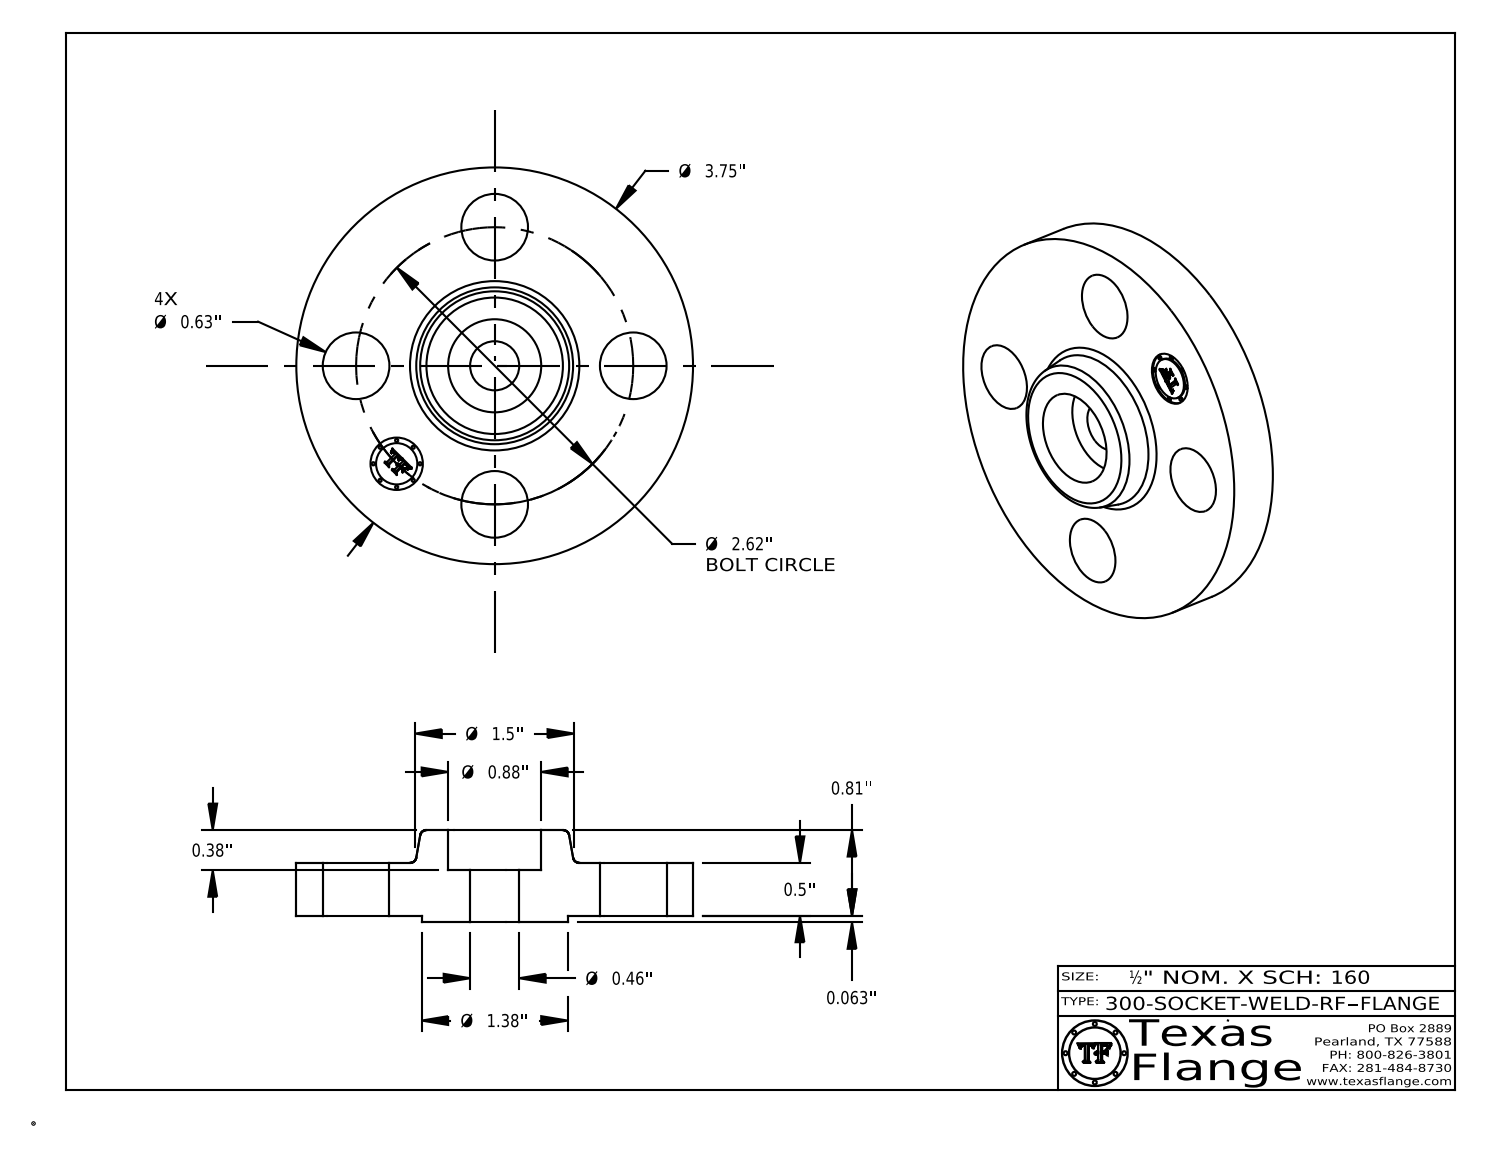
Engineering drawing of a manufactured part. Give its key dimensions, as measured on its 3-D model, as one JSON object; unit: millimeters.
{"part_name": "300-SOCKET-WELD-RF", "step_written_by": "CATIA V5 STEP AP214 (AUTOMOTIVE_DESIGN)", "units": "millimeters", "bodies": {"solids": 1, "faces": 412, "planar": 370, "cylindrical": 36, "other": 6}, "overall_size": [95.3, 95.3, 22.2], "volume_mm3": 84980, "surface_area_mm2": 20820, "round_holes": [[16, 4], [11.8, 1], [12.6, 1], [22.4, 1]], "round_bosses_or_shafts": [[0.8, 8], [95.3, 1], [35.1, 1], [9.9, 1]], "face_to_face_distances": [12.7, 1.6, 14.3, 22.1, 20.6, 7.9, 1.8, 12.5, 10.9, 9.7], "hole_center_spacings": [33.3, 47, 25.5, 61.5, 66.5, 33.3]}
